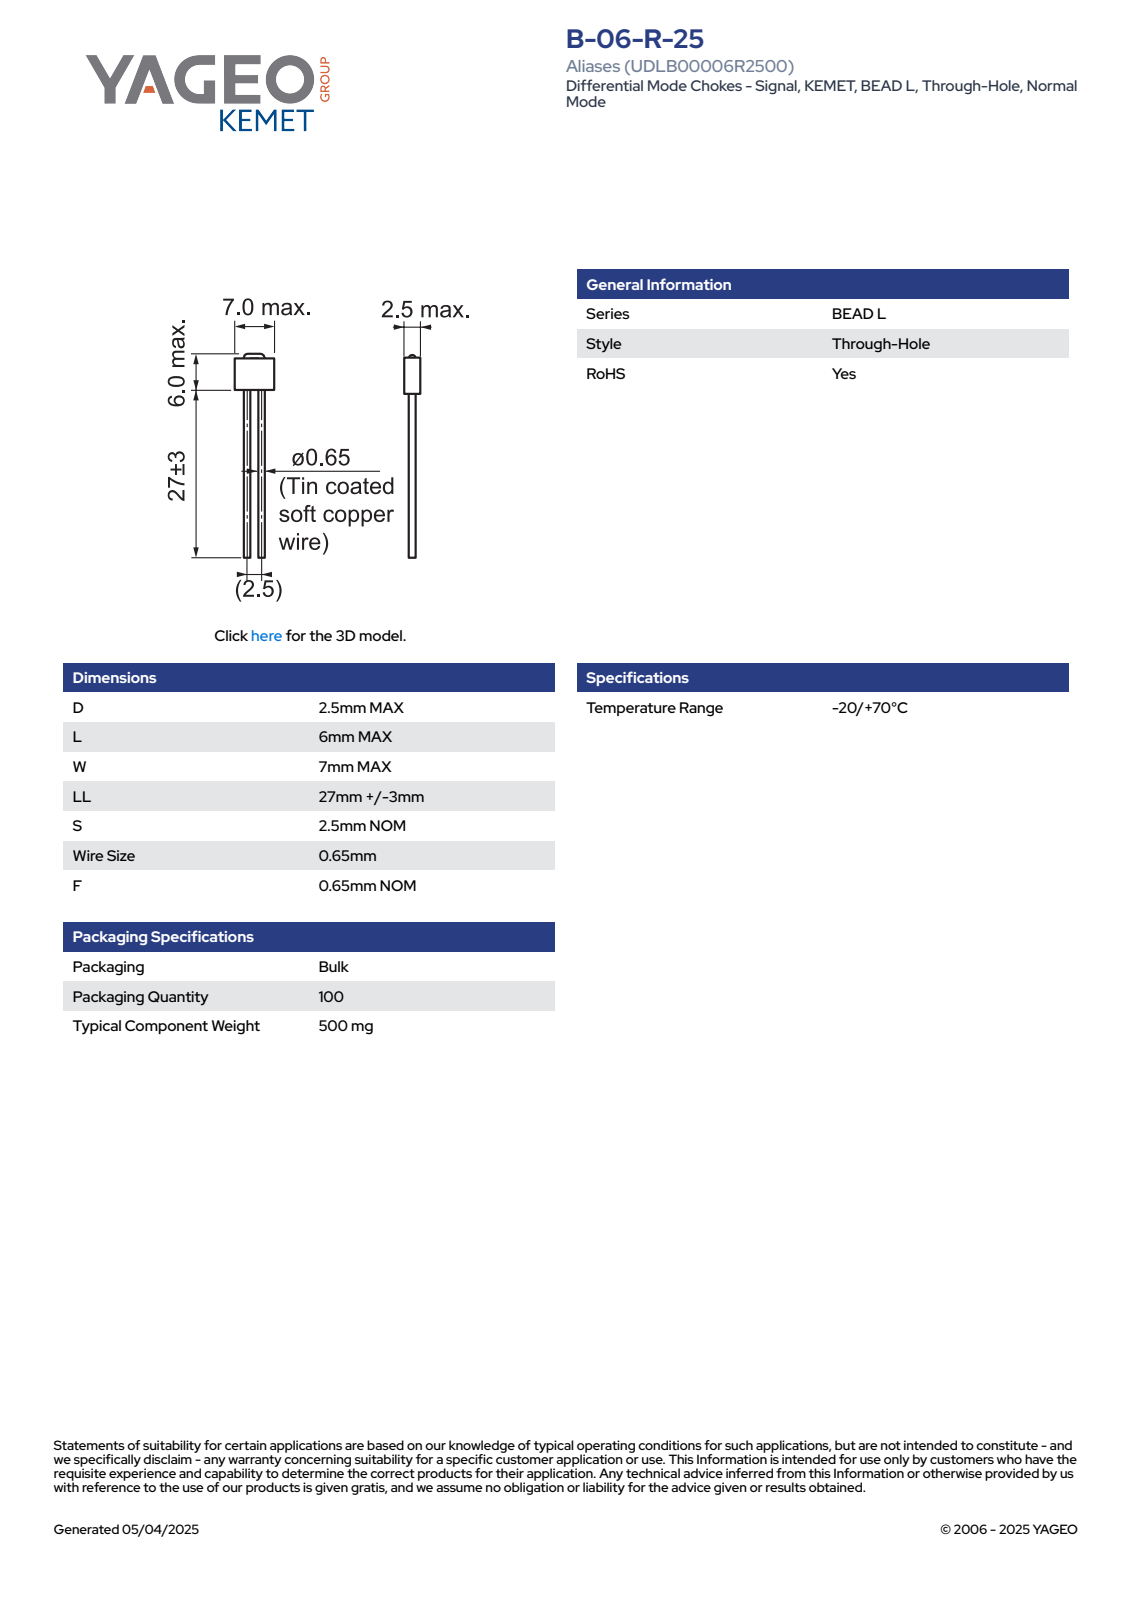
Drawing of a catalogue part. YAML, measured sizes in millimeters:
part_name: "IL_KEM_B_D2.5L6W7S2.5LL30"
step_written_by: "SolidWorks 2014 (AUTOMOTIVE_DESIGN)"
units: millimeters
bodies: {solids: 1, faces: 77, planar: 63, cylindrical: 8, other: 6}
overall_size: [36, 7, 2.5]
volume: 110
surface_area: 254
round_bosses_or_shafts:
  - {diameter: 0.65, count: 2}
partial_cylinders:
  - {radius: 1, count: 4}
face_to_face_distances: [2.5, 5.35, 7, 30, 35.35, 2.27, 3.08, 0.81, 33.08, 32.27]
